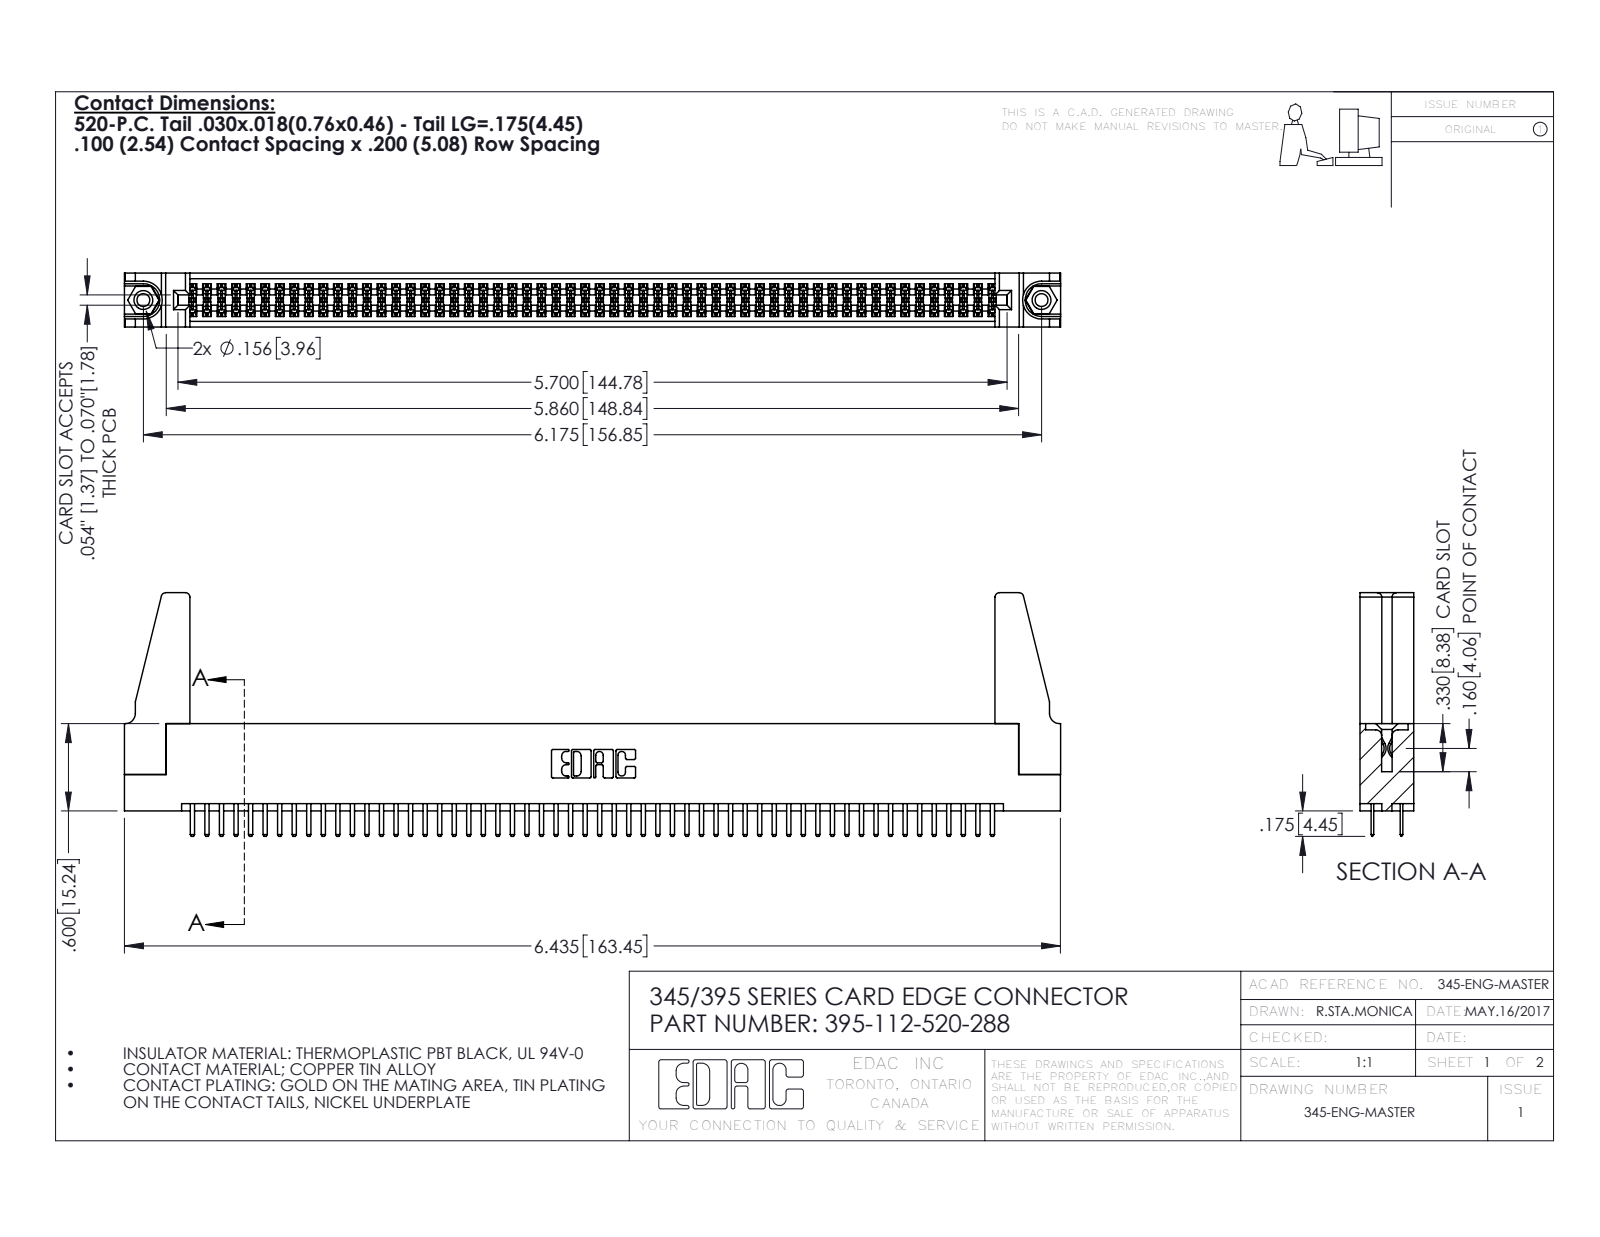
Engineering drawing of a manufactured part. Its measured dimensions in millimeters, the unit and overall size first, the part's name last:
Units: millimetres
Overall size (bounding box): 163.5 × 42.5 × 9.4
Round holes (diameter × count): ⌀2.3 ×2, ⌀3.2 ×2, ⌀4 ×2, ⌀1.6 ×1
Round bosses / shafts (diameter × count): ⌀3.9 ×2
Partial cylindrical surfaces — rounded edges, fillets, slot ends (radius × count): R0.2 ×168, R0.3 ×116, R0.3 ×22, R0.8 ×8, R0.2 ×6, R0.8 ×6, R0.7 ×3, R0.4 ×2
Main face-to-face distances: 1.8, 7.6, 9.4, 5.1, 2.5, 6.9, 0.6, 5.7, 0.6, 1.8
Hole centre spacings: 6.9, 150.9, 156.8
Volume: 19 210 mm³ · Surface area: 26 880 mm²
Bodies: 117 solids, 6298 faces (4072 planar, 2210 cylindrical, 16 other)
Part name (STEP PRODUCT): 345-292-001_345-293-120; 345-220-078_345-220-088; 395-112-520-288; 345 Part_Flush Mounting Lugs - 0.156 Dia-TH (+1 more)
STEP written by: SolidWorks 2016 (CONFIG_CONTROL_DESIGN)
